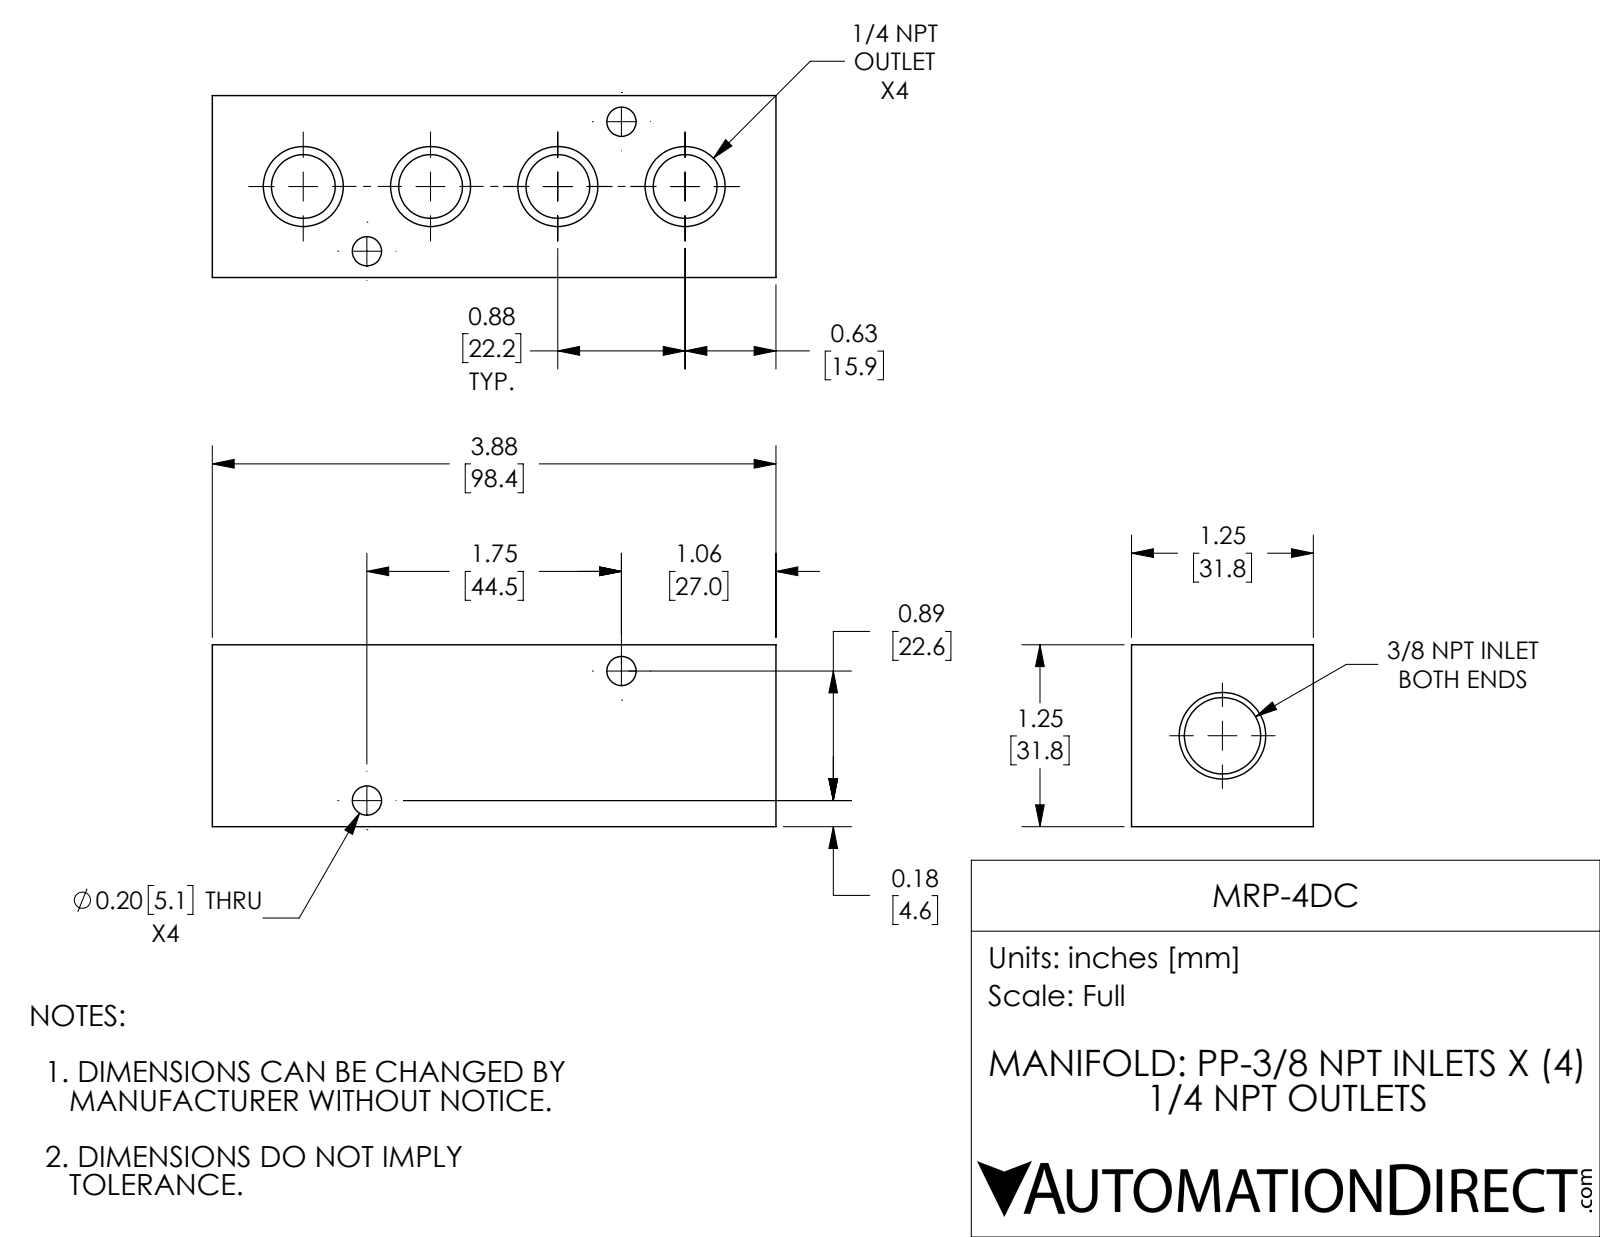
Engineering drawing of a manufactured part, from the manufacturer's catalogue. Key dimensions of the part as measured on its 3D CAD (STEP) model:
Part name (STEP PRODUCT): MRP-4DC
STEP written by: SolidWorks 2018 (AUTOMOTIVE_DESIGN)
Units: inches
Bodies: 1 solid, 44 faces (6 planar, 26 cylindrical, 12 other)
Overall size (bounding box): 3.875 × 1.25 × 1.25
Volume: 4.823 in³ · Surface area: 31.82 in²
Round holes (diameter × count): ⌀0.201 ×4, ⌀0.438 ×4, ⌀0.525 ×1
Main face-to-face distances: 1.25, 3.875
Hole centre spacings: 0.624, 0.875, 1.963, 2.232, 0.875, 1.385, 1.386, 1.75
